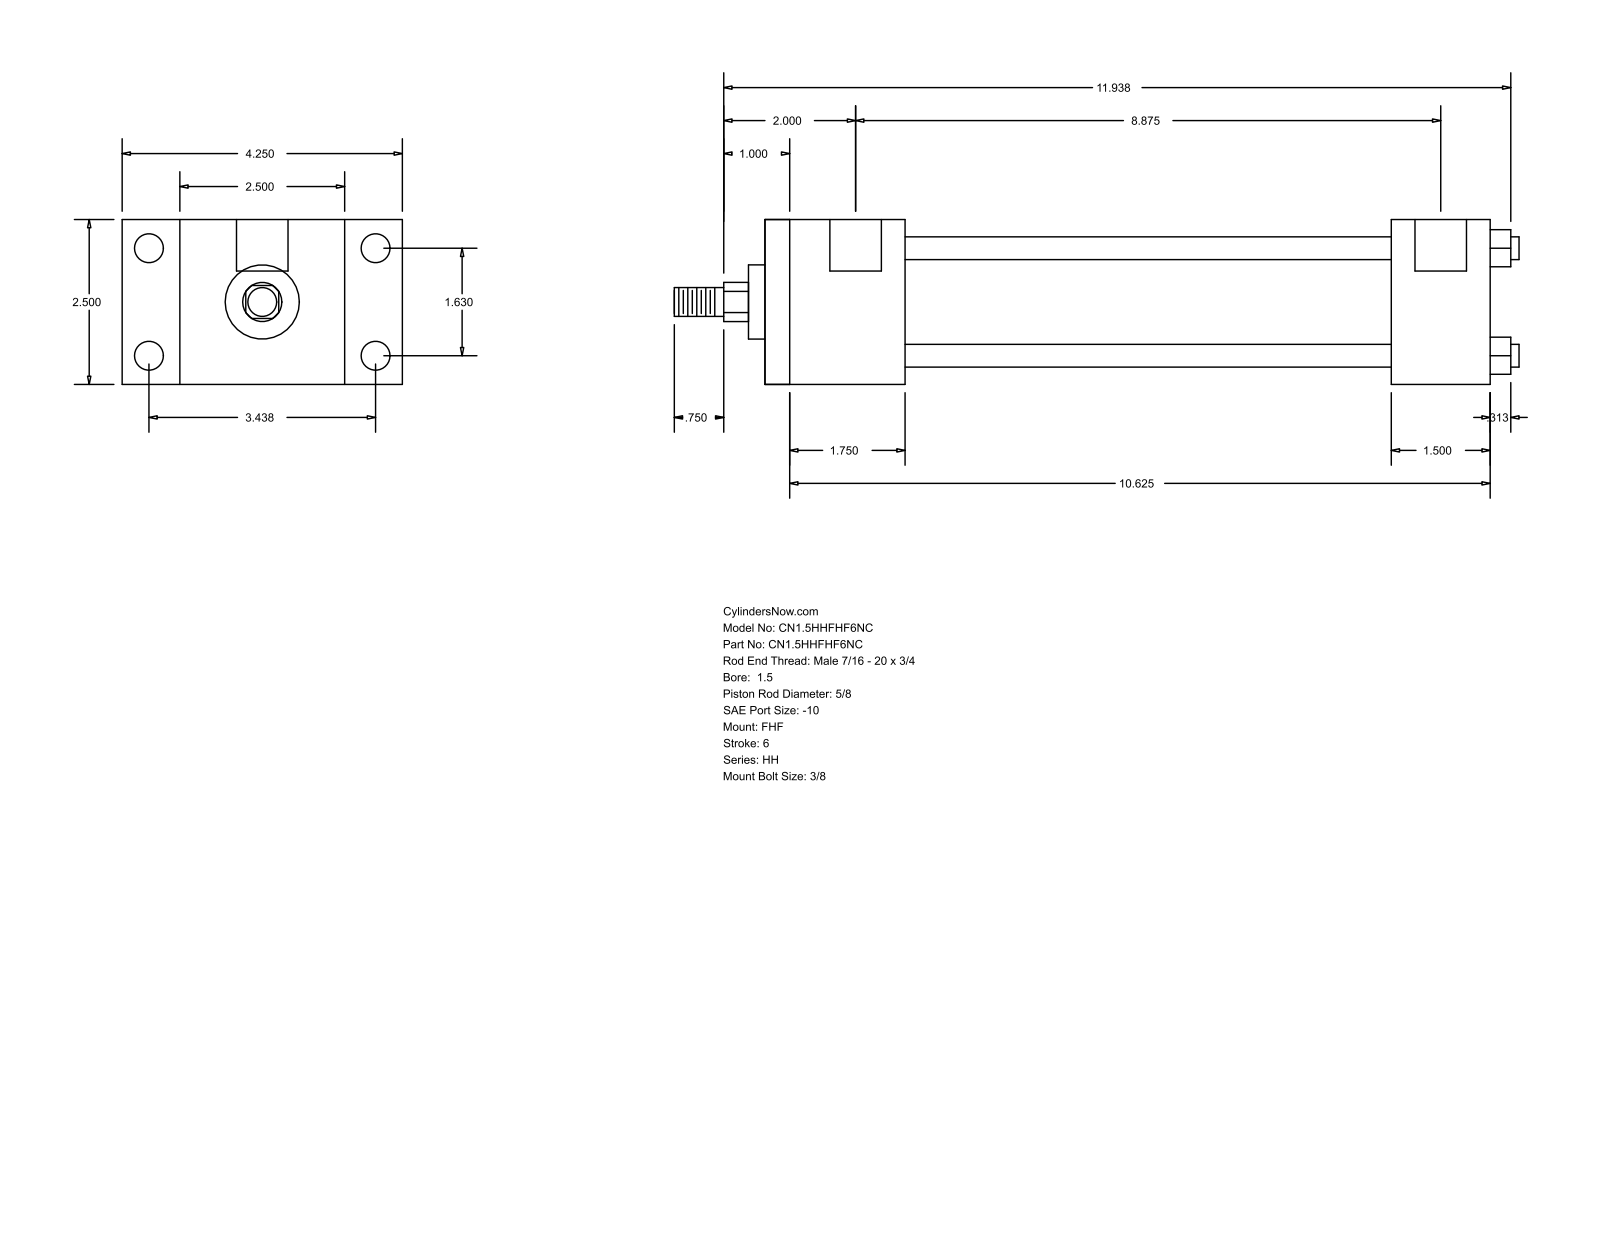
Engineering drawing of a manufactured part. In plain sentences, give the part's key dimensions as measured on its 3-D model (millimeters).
The part is named "HH_FHF__0150_0.625". Its 3-D file was written by "GSSL Pune (CONFIG_CONTROL_DESIGN)". It is 0 solids with 88 faces: 60 planar, 28 cylindrical and 0 other. Overall it measures 325.44 by 107.95 by 63.5 millimeters. Round holes: 4 of diameter 5.56, 4 of diameter 11.13, 2 of diameter 19.84. Round bosses or shafts: 4 of diameter 8.76, 1 of diameter 44.45, 1 of diameter 28.57, 1 of diameter 15.88, 1 of diameter 11.11. Partial cylindrical surfaces (rounded edges, fillets, slot ends): 1 of radius 7.54. The main face-to-face distances are 63.5, 22.23, 85.73, 53.97, 107.96, 279.39, 225.42, 241.3, 187.33, 38.09. The hole center spacings are 41.4, 87.32, 96.64, 228.6, 1.58, 1.59, 225.43, 227.01.
